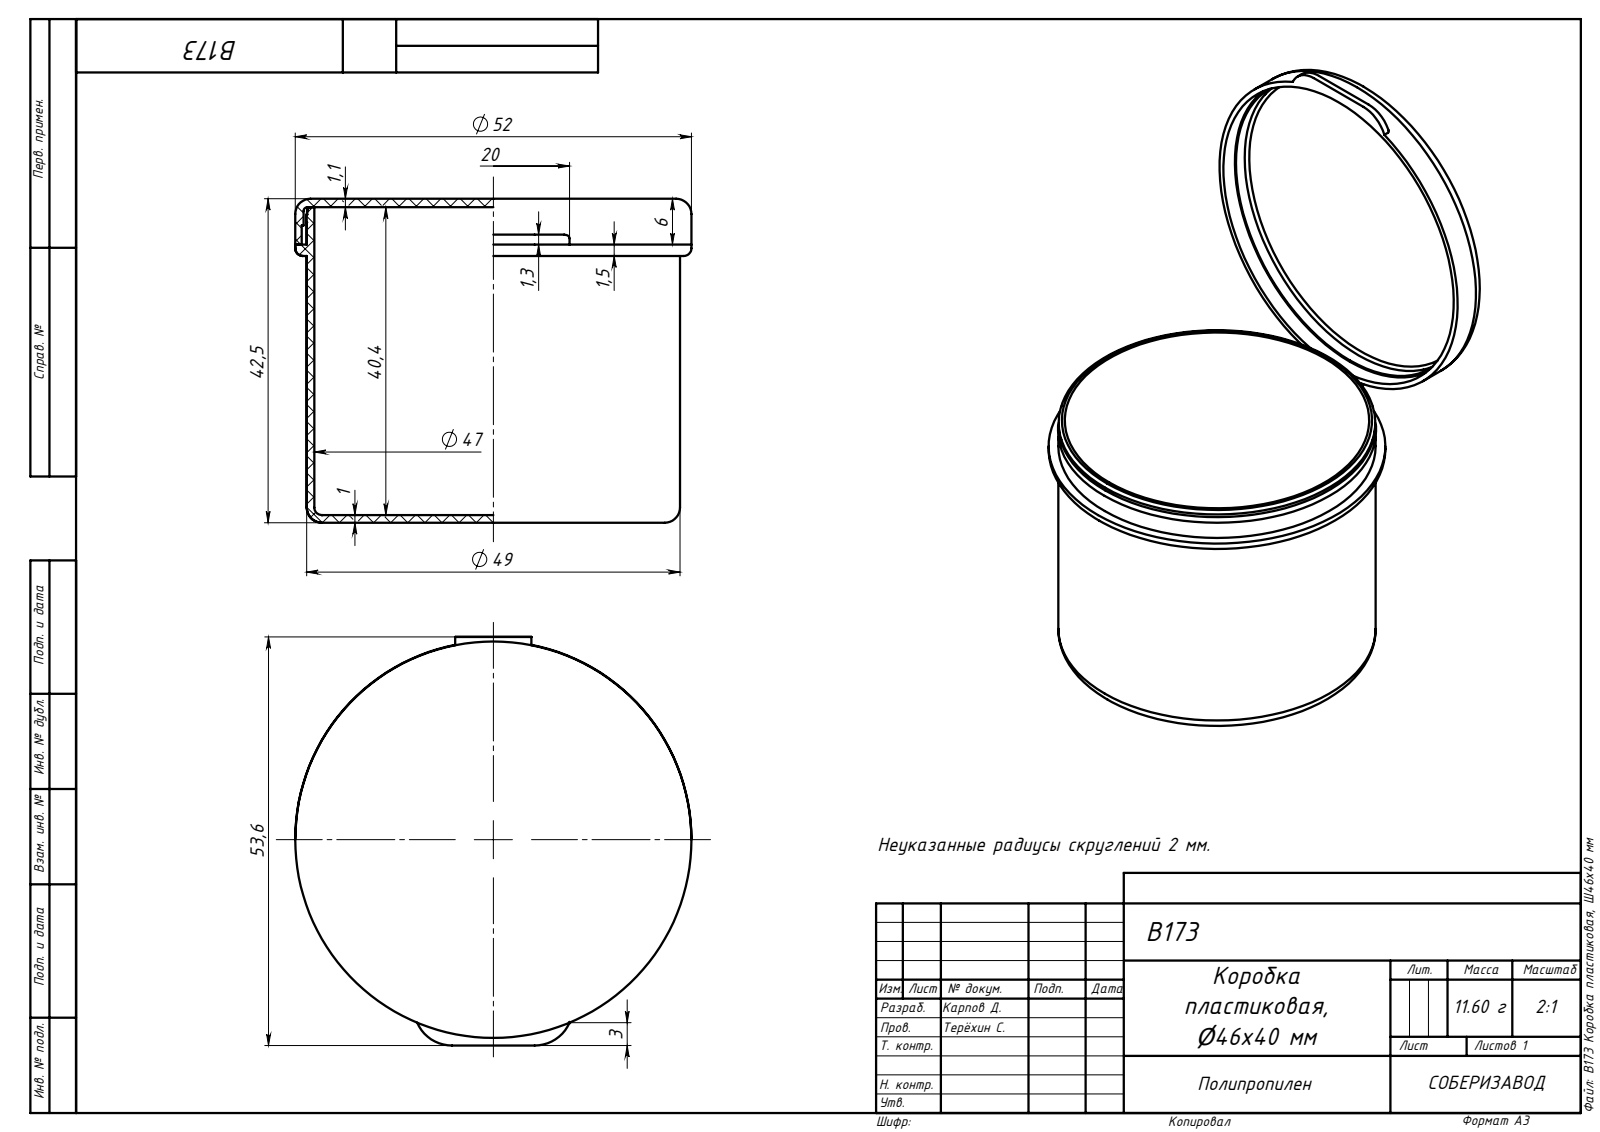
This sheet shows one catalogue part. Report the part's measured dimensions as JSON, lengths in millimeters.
{"part_name": "B173 Крышка; B173 Емкость; B173 Коробка пластиковая, O46x40 мм", "step_written_by": "SolidWorks 2020 (AUTOMOTIVE_DESIGN)", "units": "millimeters", "bodies": {"solids": 3, "faces": 58, "planar": 23, "cylindrical": 21, "other": 14}, "overall_size": [53.6, 52, 42.5], "volume_mm3": 11201, "surface_area_mm2": 22230, "round_holes": [[47, 1], [49.8, 1], [50.3, 1]], "round_bosses_or_shafts": [[52, 2], [49.1, 1], [49, 1], [48.89, 1]], "partial_cylinders_radius": [[5, 2], [0.5, 1]], "face_to_face_distances": [1.1, 1, 40.4, 41.4, 42.5, 41.5, 36.5, 35.5, 4.9, 6]}
